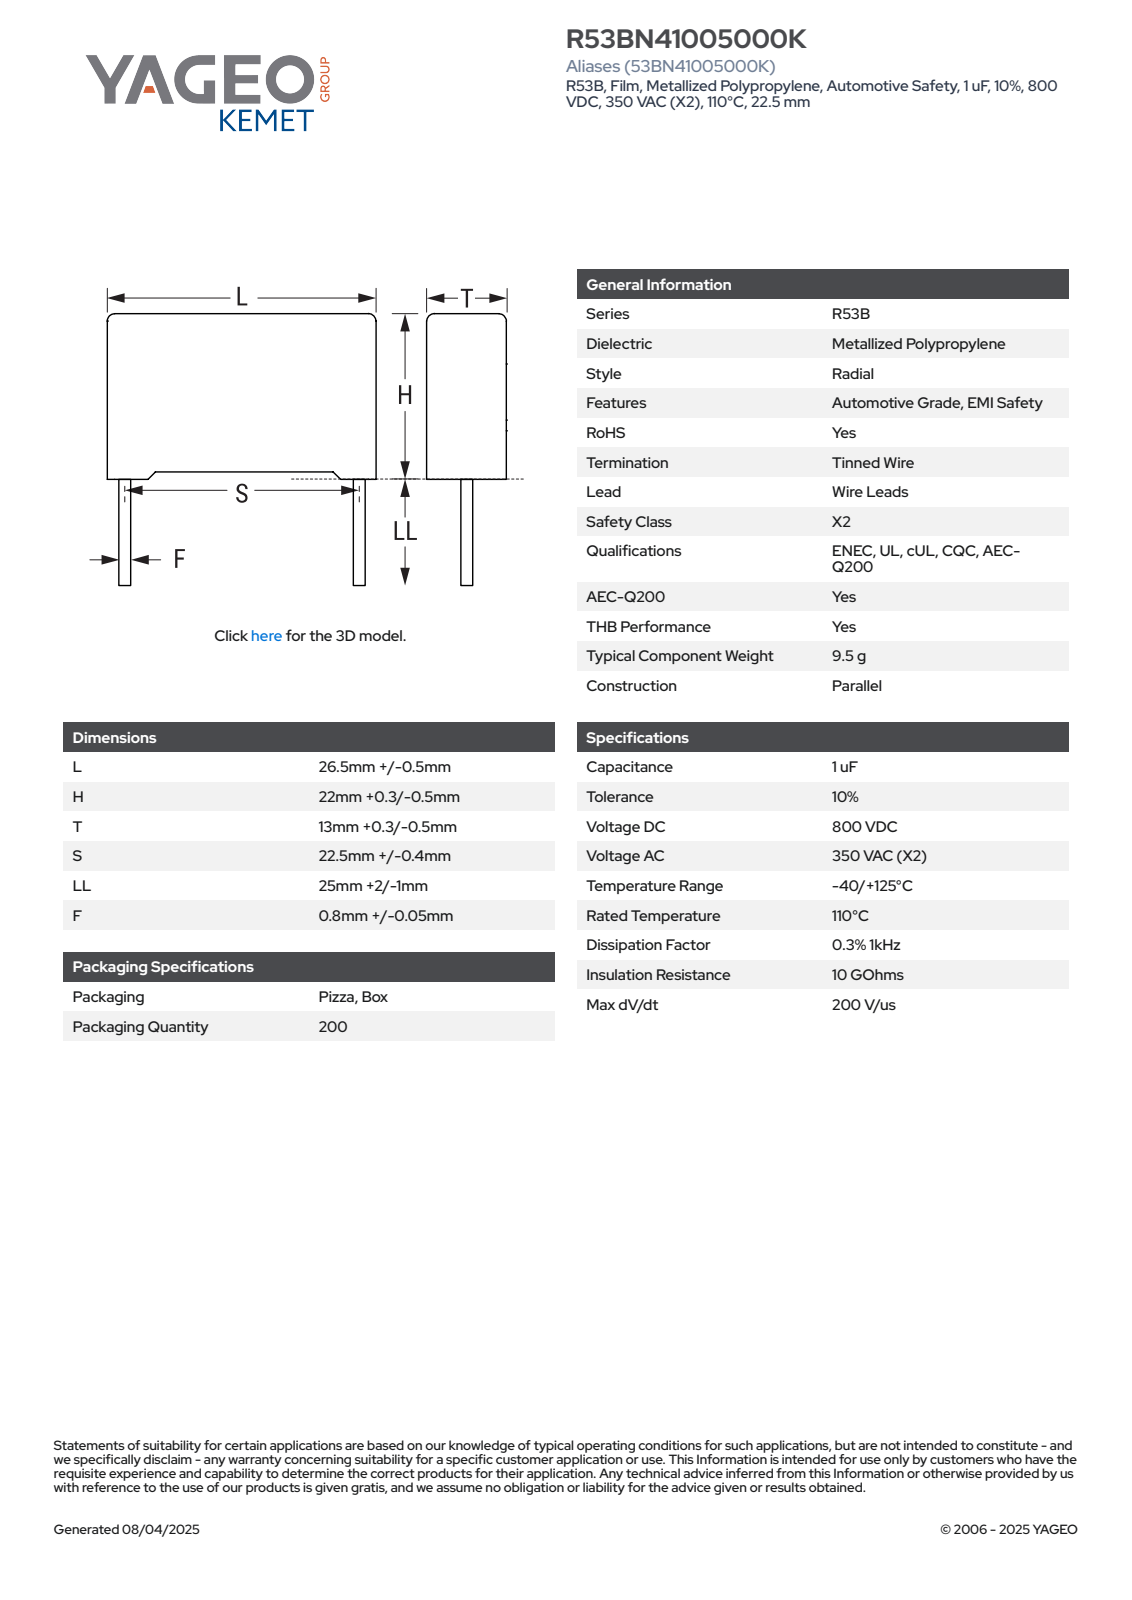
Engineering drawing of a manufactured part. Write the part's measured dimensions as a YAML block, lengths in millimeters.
part_name: "CFR_RB2_26.5X22X13_L27H22.3T13.3S22.5LL27F0.85"
step_written_by: "SolidWorks 2021 (AUTOMOTIVE_DESIGN)"
units: millimeters
bodies: {solids: 4, faces: 85, planar: 77, cylindrical: 8, other: 0}
overall_size: [49.3, 27, 13.3]
volume: 7788
surface_area: 2700
round_bosses_or_shafts:
  - {diameter: 0.85, count: 2}
partial_cylinders:
  - {radius: 0.5, count: 4}
face_to_face_distances: [13.3, 27, 21.53, 21.55, 0.75, 0.77, 22.3, 0.9, 26.1, 13.31]
